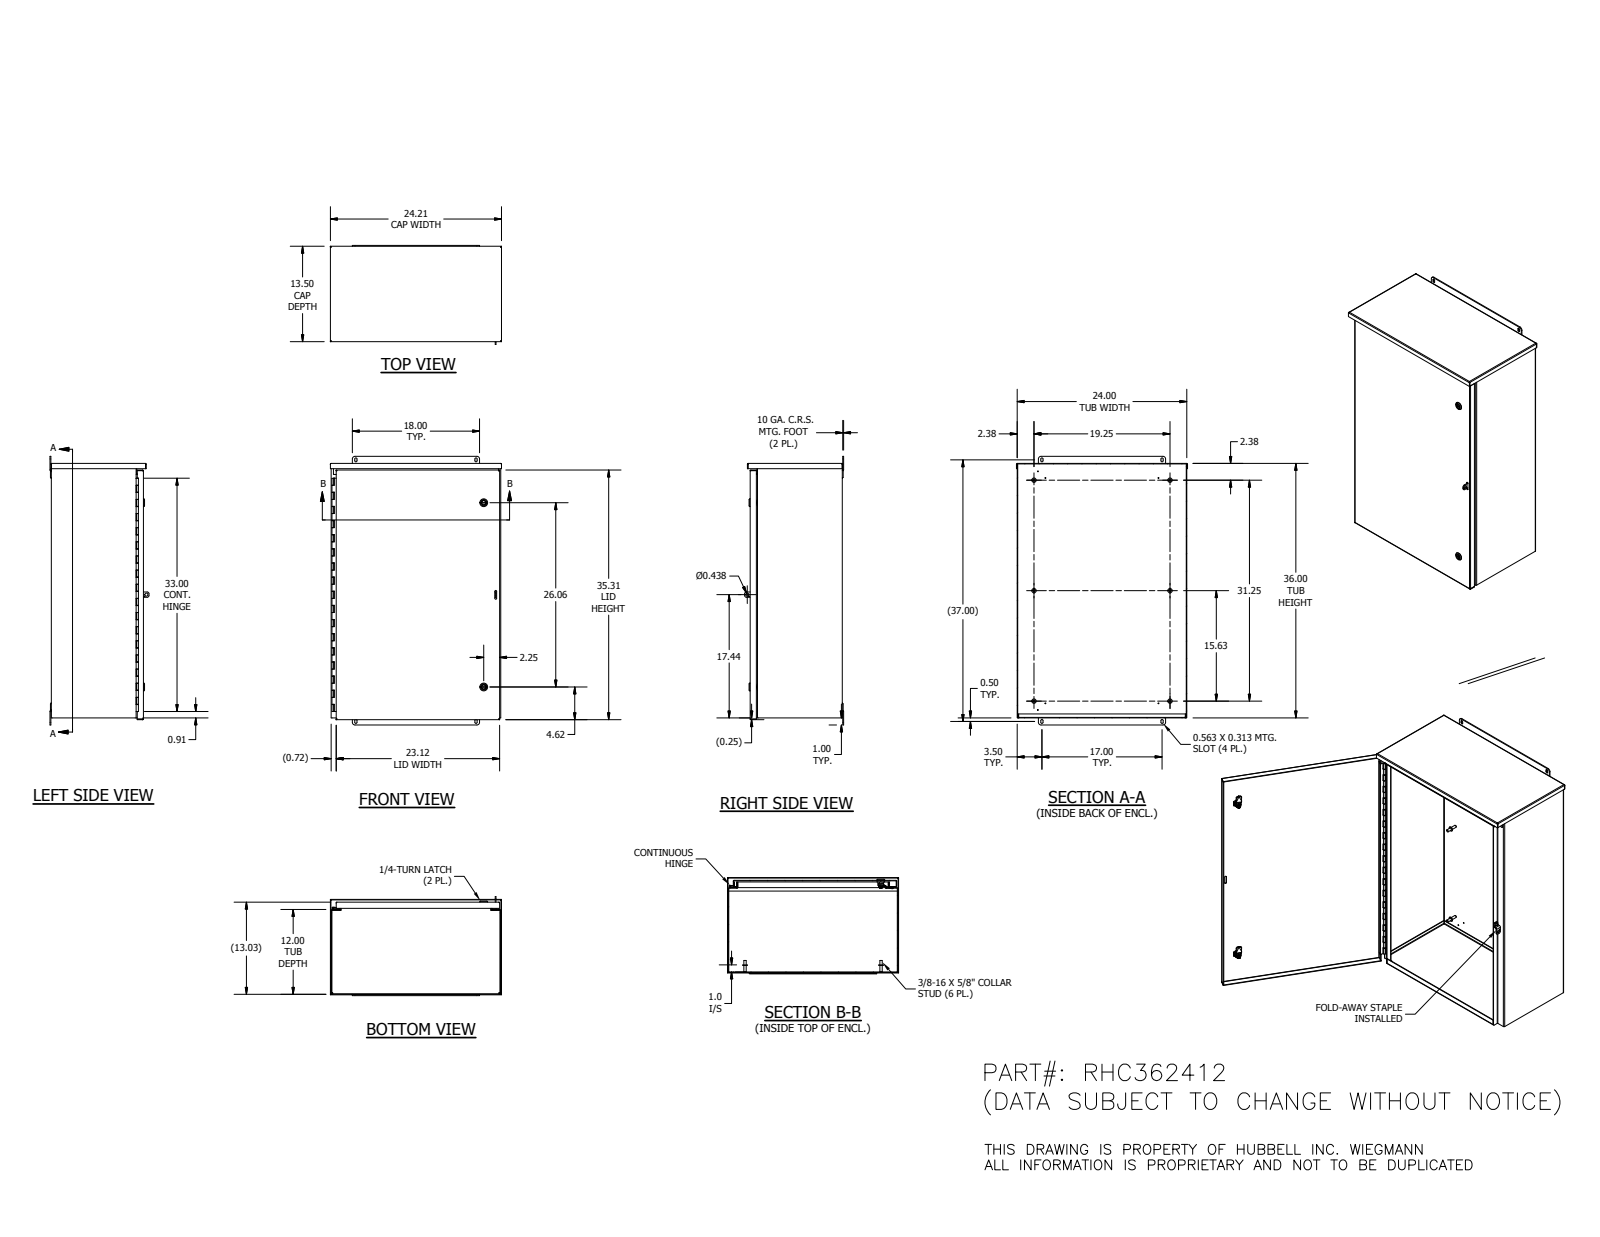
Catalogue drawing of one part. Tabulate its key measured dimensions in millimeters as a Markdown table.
| quantity | value |
| --- | --- |
| part name | RHC362412BLR; RHC24TOP; RHC2412BTM; RHC3624LID (+8 more) |
| STEP written by | Autodesk Inventor 2016 (AUTOMOTIVE_DESIGN) |
| units | millimeters |
| bodies | 32 solids, 1484 faces (854 planar, 478 cylindrical, 152 other) |
| overall size | 965.2 × 614.95 × 355.9 |
| volume | 4 645 000 mm³ |
| surface area | 4 890 000 mm² |
| round holes (diameter × count) | 3.05 × 6, 3.17 × 2, 5 × 2, 8 × 2, 10 × 2, 10.2 × 2, 16.1 × 2, 20.38 × 2, 5.03 × 1, 5.11 × 1, 11.11 × 1 |
| round bosses / shafts (diameter × count) | 15.88 × 6, 8.38 × 6, 28 × 2, 27 × 2, 23 × 2, 19.8 × 2, 15.8 × 2, 15.2 × 2 |
| partial cylindrical surfaces (radius × count) | 0.3 × 56, 0.5 × 21, 3.47 × 13, 3.17 × 10, 0.79 × 8, 1.59 × 8, 1.59 × 8, 2.67 × 8 |
| main face-to-face distances | 1.88, 329.17, 607.72, 331.05, 327.29, 912.52, 605.84, 609.6, 910.64, 914.4 |
| hole center spacings | 35.91, 406.4, 433.98, 809.75, 833.93, 906.01, 939.41, 8.98 |
